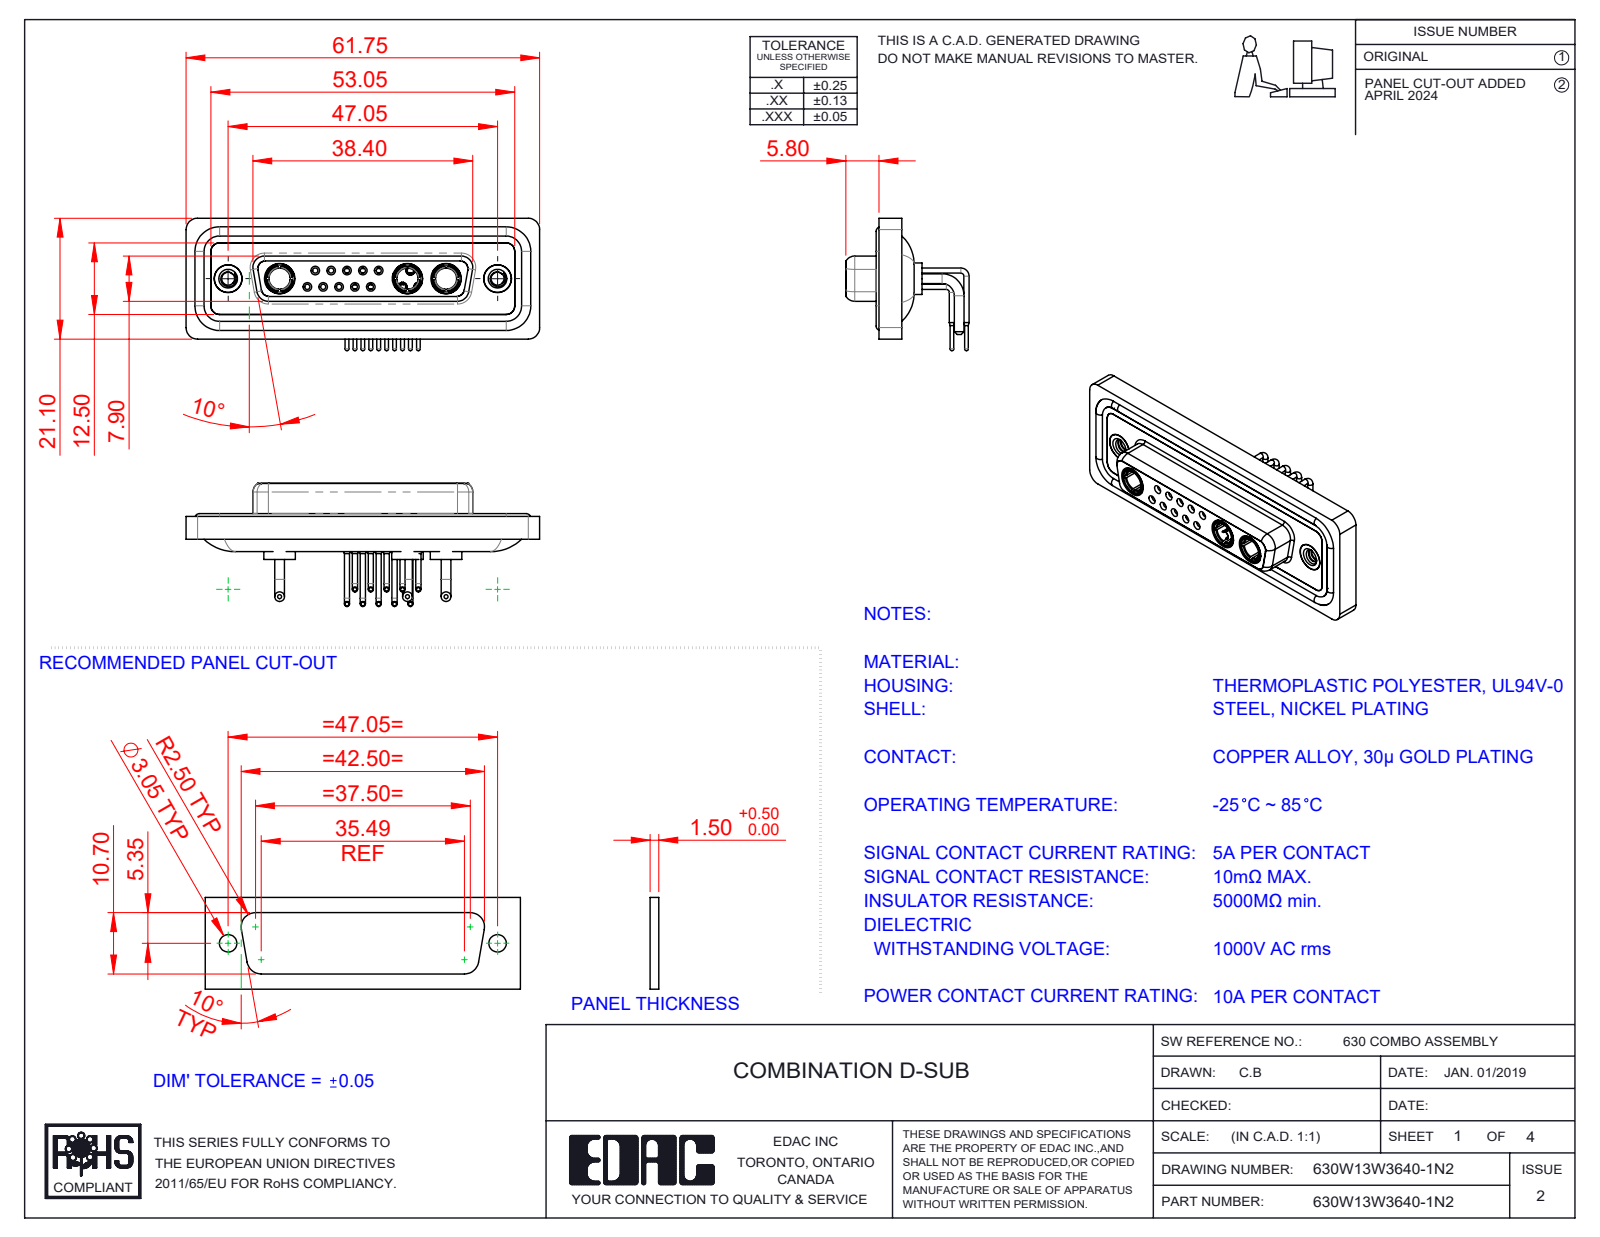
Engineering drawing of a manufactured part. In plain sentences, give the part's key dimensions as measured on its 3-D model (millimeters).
The part is named "630Combo Waterproof Housing_25 Contacts; 630Combo Contact Row 2_50 Contacts; 630W13W3640-1N2; 630Combo Shell Rear_25 Contacts (+5 more)". Its 3-D file was written by "SolidWorks 2023 (CONFIG_CONTROL_DESIGN)". It is 23 solids with 1150 faces: 342 planar, 493 cylindrical and 315 other. Overall it measures 61.75 by 23.12 by 21.53 millimeters. Its volume is 8 297 cubic millimeters and its surface area 14 144 square millimeters. Round holes: 10 of diameter 0.9, 10 of diameter 1.1, 10 of diameter 1.5, 10 of diameter 2, 5 of diameter 1.6, 5 of diameter 1.7, 5 of diameter 4.85, 3 of diameter 3.7, 3 of diameter 5.3, 2 of diameter 2.26, 2 of diameter 4, 2 of diameter 4.05. Round bosses or shafts: 15 of diameter 0.9, 12 of diameter 1.6, 10 of diameter 0.65, 6 of diameter 1.7, 5 of diameter 2, 5 of diameter 1.5, 3 of diameter 5.5, 3 of diameter 5.2. Partial cylindrical surfaces (rounded edges, fillets, slot ends): 18 of radius 1.5, 18 of radius 2, 8 of radius 1.35, 8 of radius 1.6, 4 of radius 0.25, 4 of radius 0.5, 4 of radius 0.6, 4 of radius 0.65. The main face-to-face distances are 0.4, 1.8, 4.1, 1.1, 1.6, 1.5, 3.1, 2.5, 3.7, 1.4. The hole center spacings are 3.16, 2.77, 5.54, 5.04, 8.31, 5.03, 7.49, 11.08.
